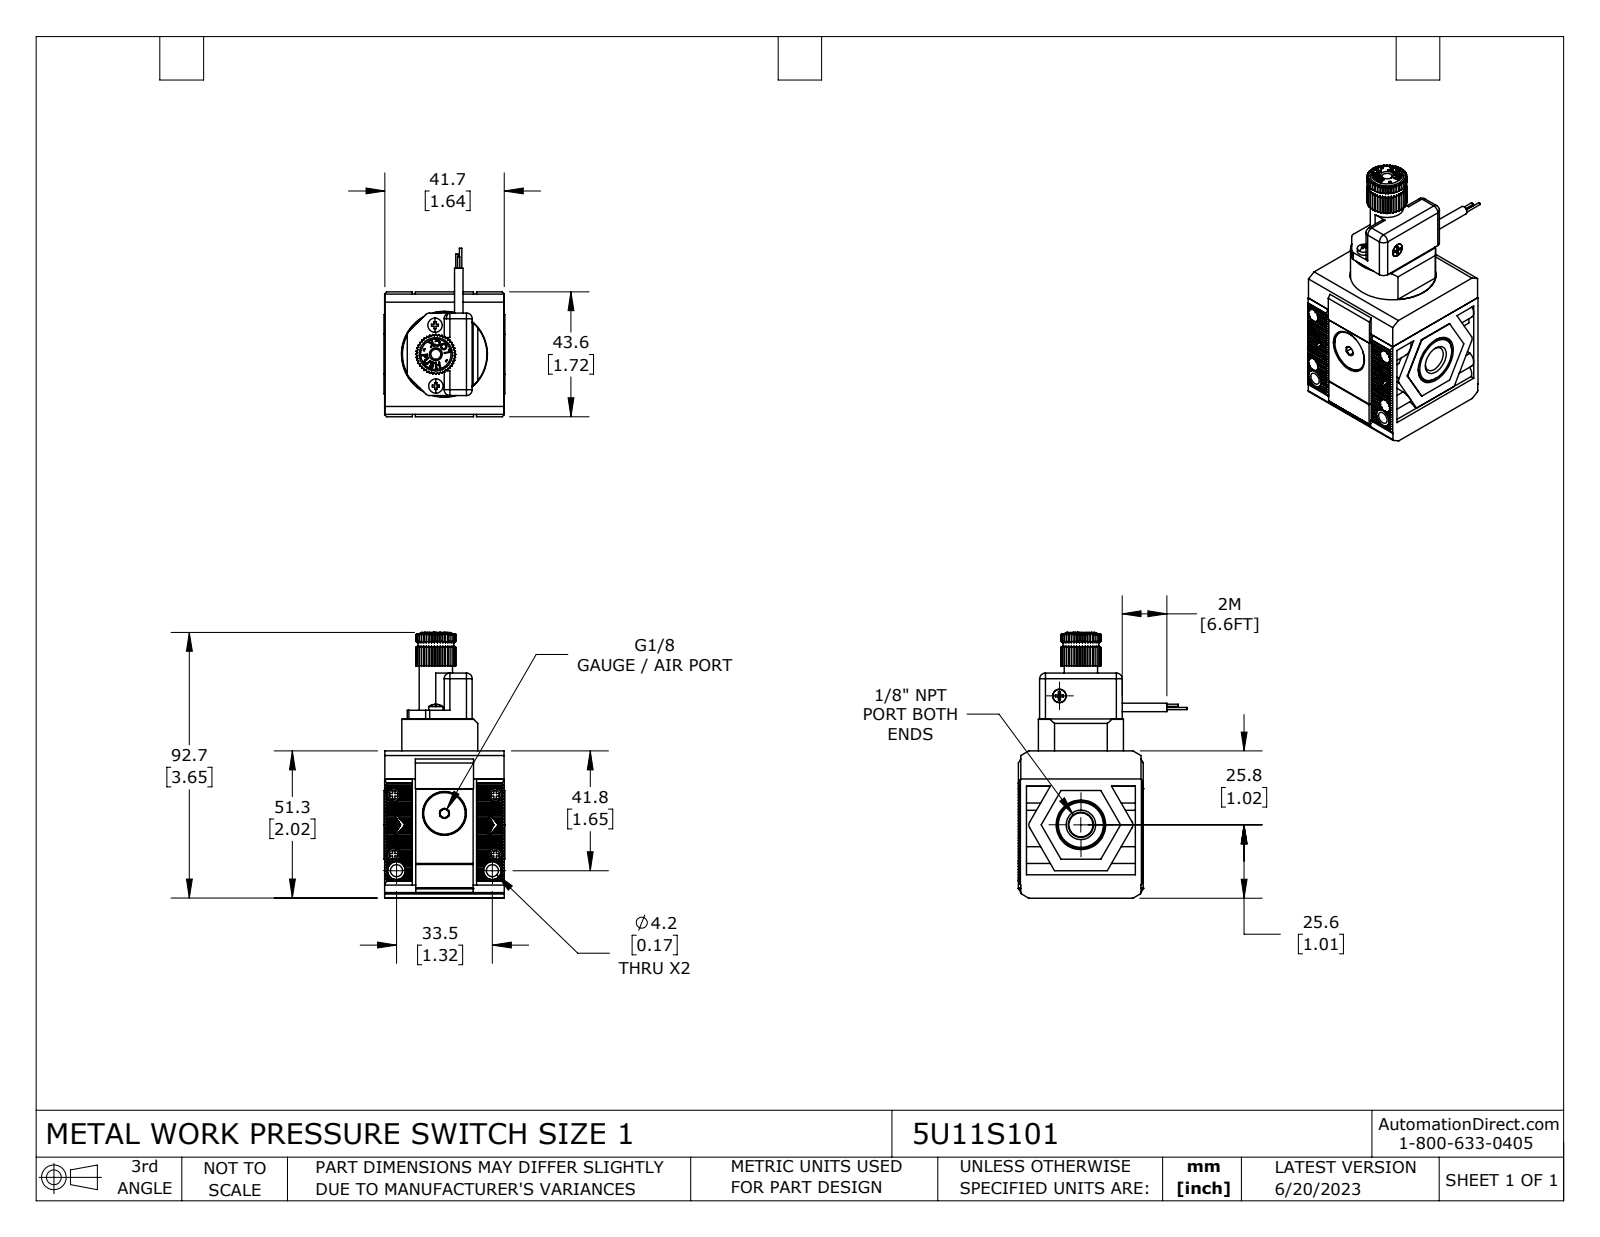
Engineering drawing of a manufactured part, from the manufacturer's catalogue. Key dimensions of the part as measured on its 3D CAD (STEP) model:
Part name (STEP PRODUCT): 5U11S101
STEP written by: SolidWorks 2021 (CONFIG_CONTROL_DESIGN)
Units: inches
Bodies: 13 solids, 1575 faces (1086 planar, 298 cylindrical, 191 other)
Overall size (bounding box): 3.654 × 2.315 × 1.661
Volume: 6.291 in³ · Surface area: 54.79 in²
Round holes (diameter × count): ⌀0.083 ×4, ⌀0.118 ×4, ⌀0.185 ×4, ⌀0.165 ×2, ⌀0.071 ×1, ⌀0.337 ×1, ⌀0.602 ×1, ⌀1.181 ×1, ⌀1.26 ×1
Round bosses / shafts (diameter × count): ⌀0.181 ×5, ⌀0.102 ×4, ⌀0.031 ×3, ⌀0.244 ×2, ⌀0.197 ×2, ⌀1.169 ×1, ⌀0.898 ×1, ⌀0.717 ×1
Partial cylindrical surfaces — rounded edges, fillets, slot ends (radius × count): R0.079 ×14, R0.024 ×4, R0.122 ×4, R0.008 ×2, R0.008 ×1, R0.009 ×1, R0.009 ×1, R0.009 ×1
Main face-to-face distances: 1.638, 1.339, 0.307, 1.642, 1.673, 1.654, 0.386, 0.043, 0.315, 0.031
Hole centre spacings: 0.222, 0.742, 0.823, 0.9, 1.027, 1.042, 1.374, 1.394
